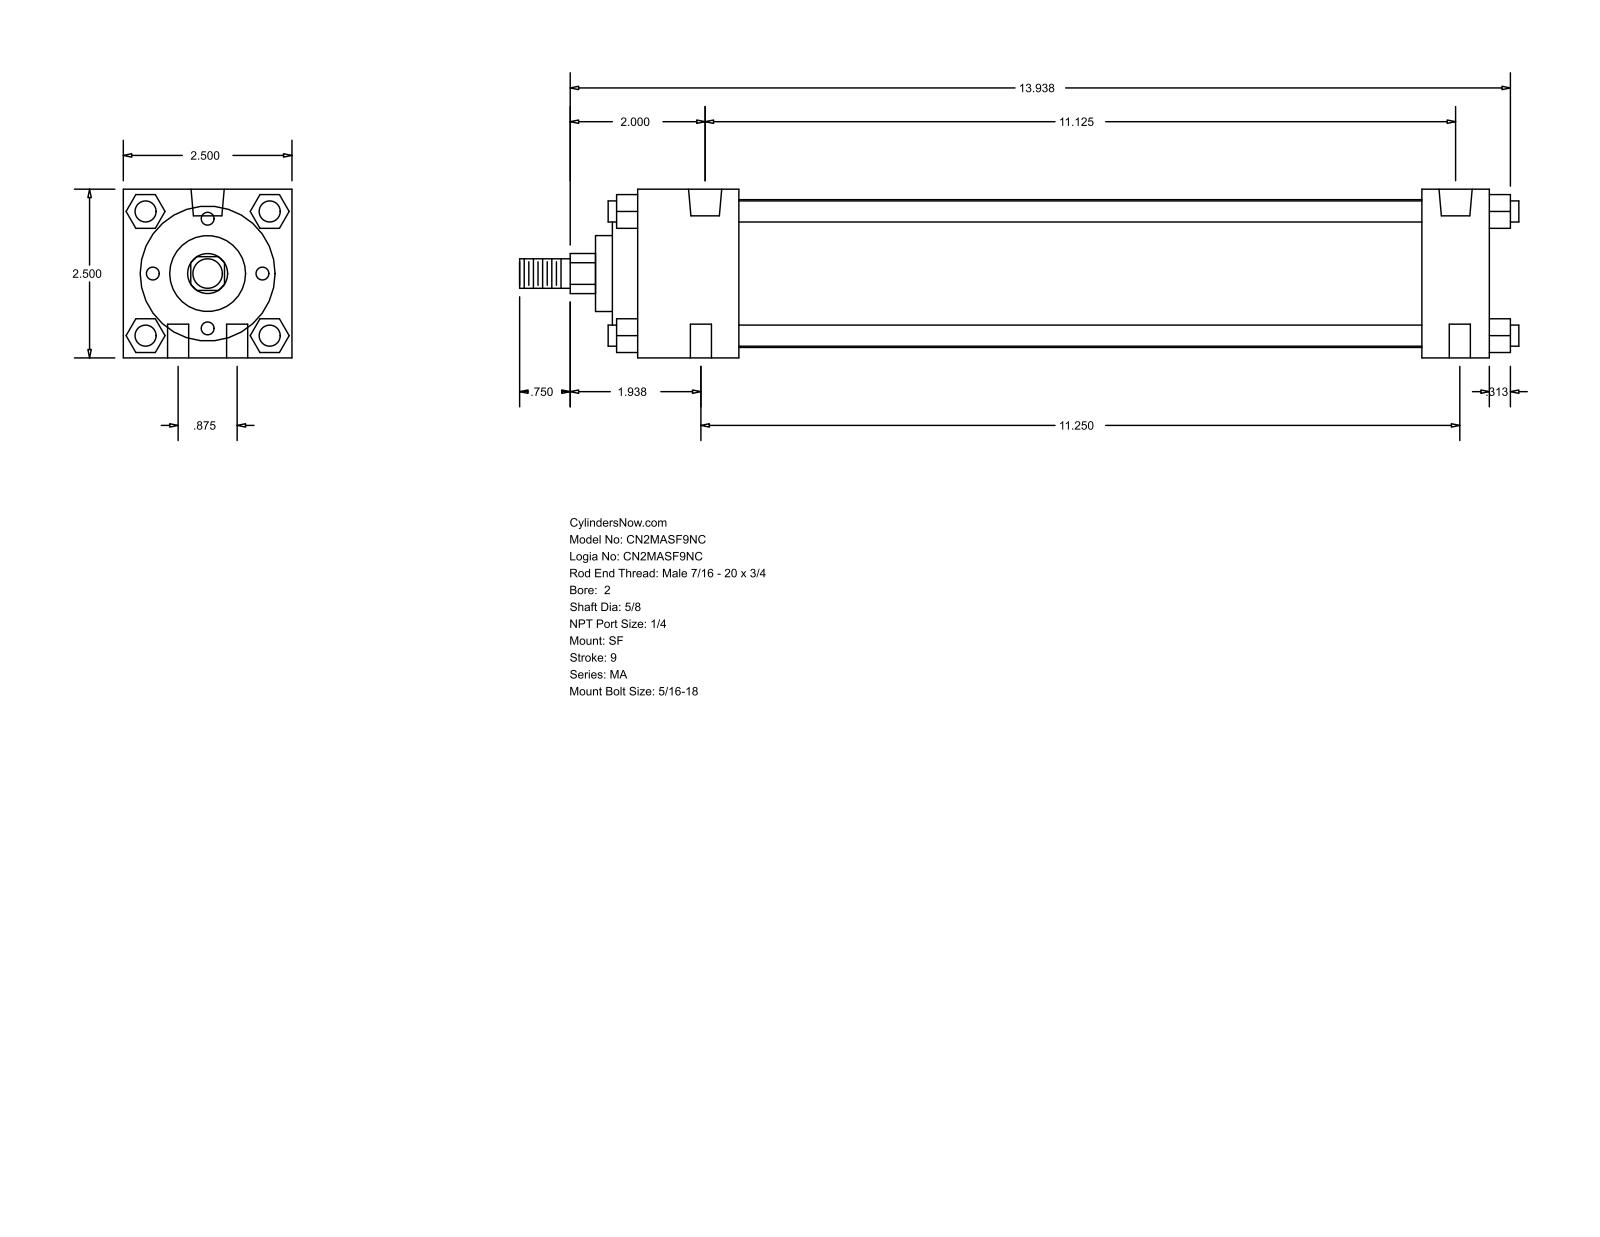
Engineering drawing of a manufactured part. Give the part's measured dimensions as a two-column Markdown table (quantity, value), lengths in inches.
| quantity | value |
| --- | --- |
| part name | MA_SF__0200_0.625 |
| STEP written by | GSSL Pune (CONFIG_CONTROL_DESIGN) |
| units | inches |
| bodies | 0 solids, 126 faces (95 planar, 31 cylindrical, 0 other) |
| overall size | 14.813 × 2.5 × 2.5 |
| round holes (diameter × count) | 0.313 × 6, 0.492 × 2 |
| round bosses / shafts (diameter × count) | 0.313 × 4, 2.19 × 1, 2 × 1, 1.125 × 1, 0.625 × 1, 0.437 × 1 |
| partial cylindrical surfaces (radius × count) | 0.297 × 1 |
| main face-to-face distances | 2.5, 0.5, 1.5, 12.625, 11.625, 1, 10.125, 11.125, 0.375, 1.875 |
| hole center spacings | 0.442, 0.875, 11.125, 11.196, 11.196, 11.25, 11.284 |
